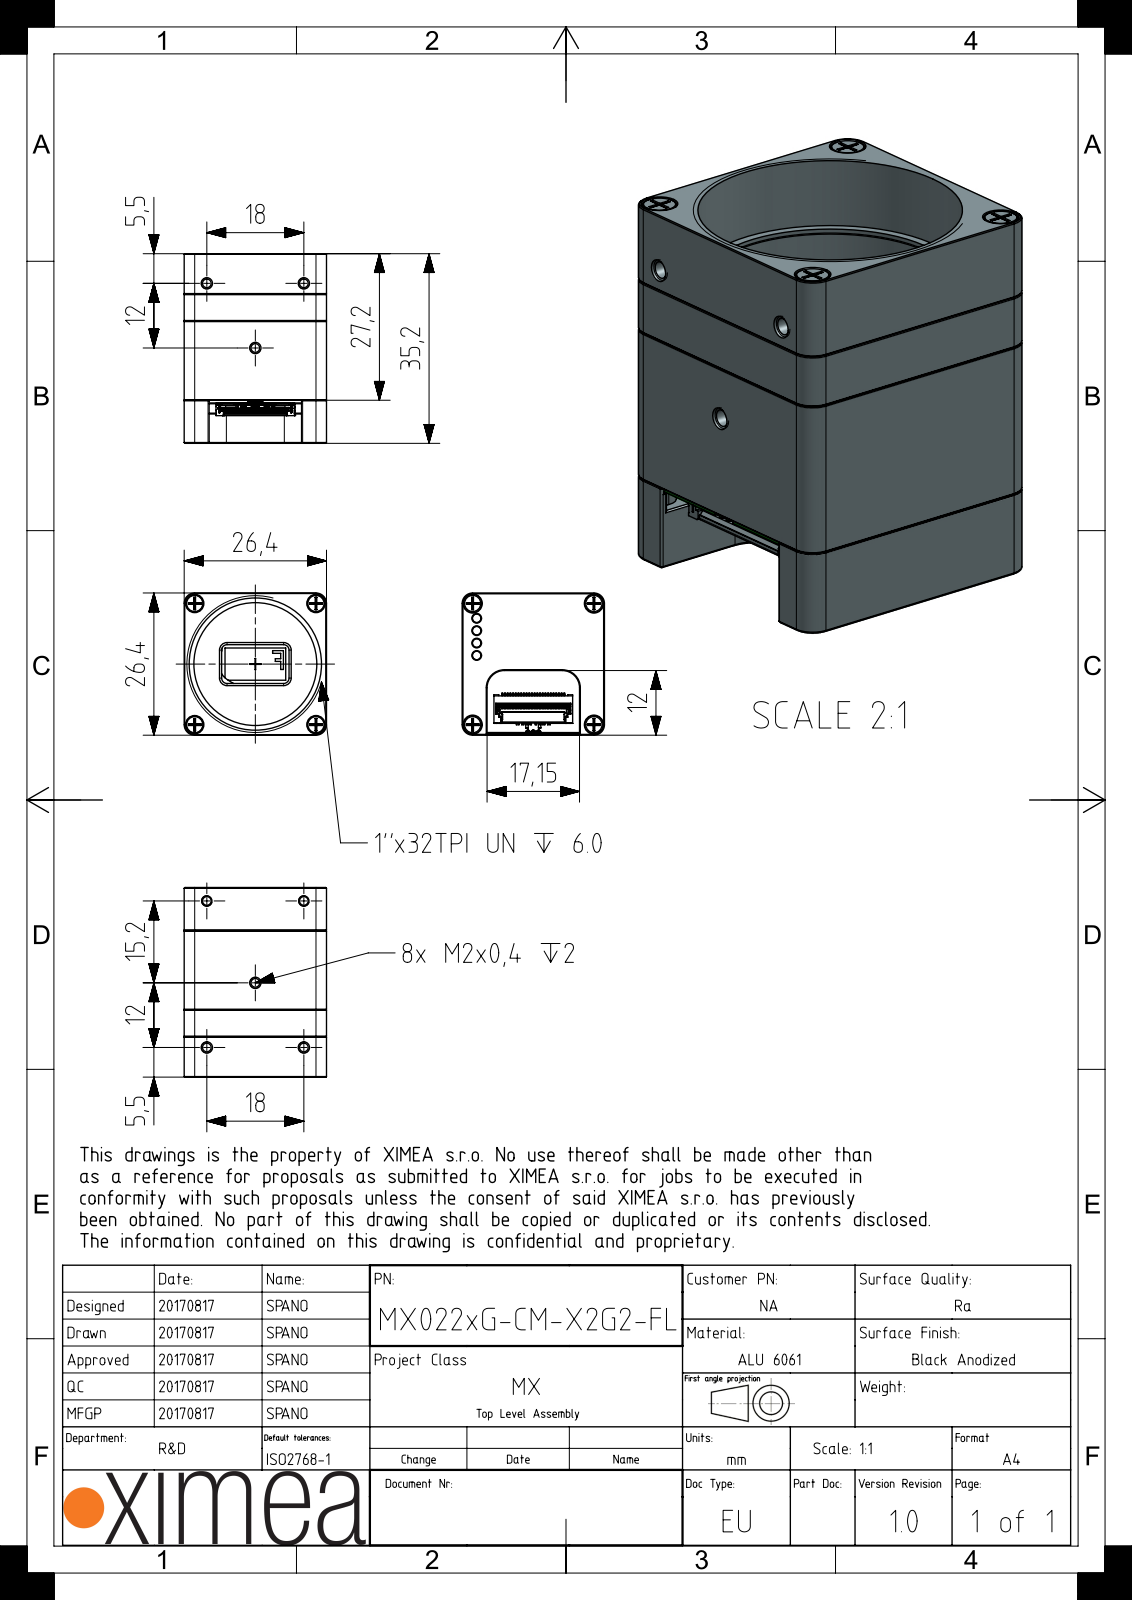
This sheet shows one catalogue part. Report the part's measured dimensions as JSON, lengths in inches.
{"part_name": "CMV2000_Glass; CMV2000_Package; MECH-O-RING-22X1-VI370; FLT-BK7-AR2X-D25 (+8 more)", "step_written_by": "SIEMENS PLM Software NX 1907 (AUTOMOTIVE_DESIGN)", "units": "inches", "bodies": {"solids": 135, "faces": 7968, "planar": 5279, "cylindrical": 2317, "other": 372}, "overall_size": [1.386, 1.039, 1.039], "volume_in3": 0.694, "surface_area_in2": 29.57, "round_holes": [[0.03, 95], [0.063, 13], [0.02, 5], [0.035, 4], [0.071, 4], [0.079, 4], [0.083, 4], [0.118, 4], [0.126, 4], [0.132, 4], [0.051, 2], [0.827, 1]], "round_bosses_or_shafts": [[0.012, 95], [0.075, 4], [0.064, 4], [0.033, 4], [0.118, 2], [0.063, 2], [0.984, 1], [0.85, 1]], "partial_cylinders_radius": [[0.039, 20], [0.059, 19], [0.015, 18], [0.013, 17], [0.051, 16], [0.006, 14], [0.008, 14], [0.004, 10]], "face_to_face_distances": [0.039, 1.039, 0.142, 0.437, 0.305, 0.622, 0.583, 0.579, 0.181, 0.441], "hole_center_spacings": [0.05, 0.071, 0.1, 0.112, 0.15, 0.158, 0.206, 0.559]}
